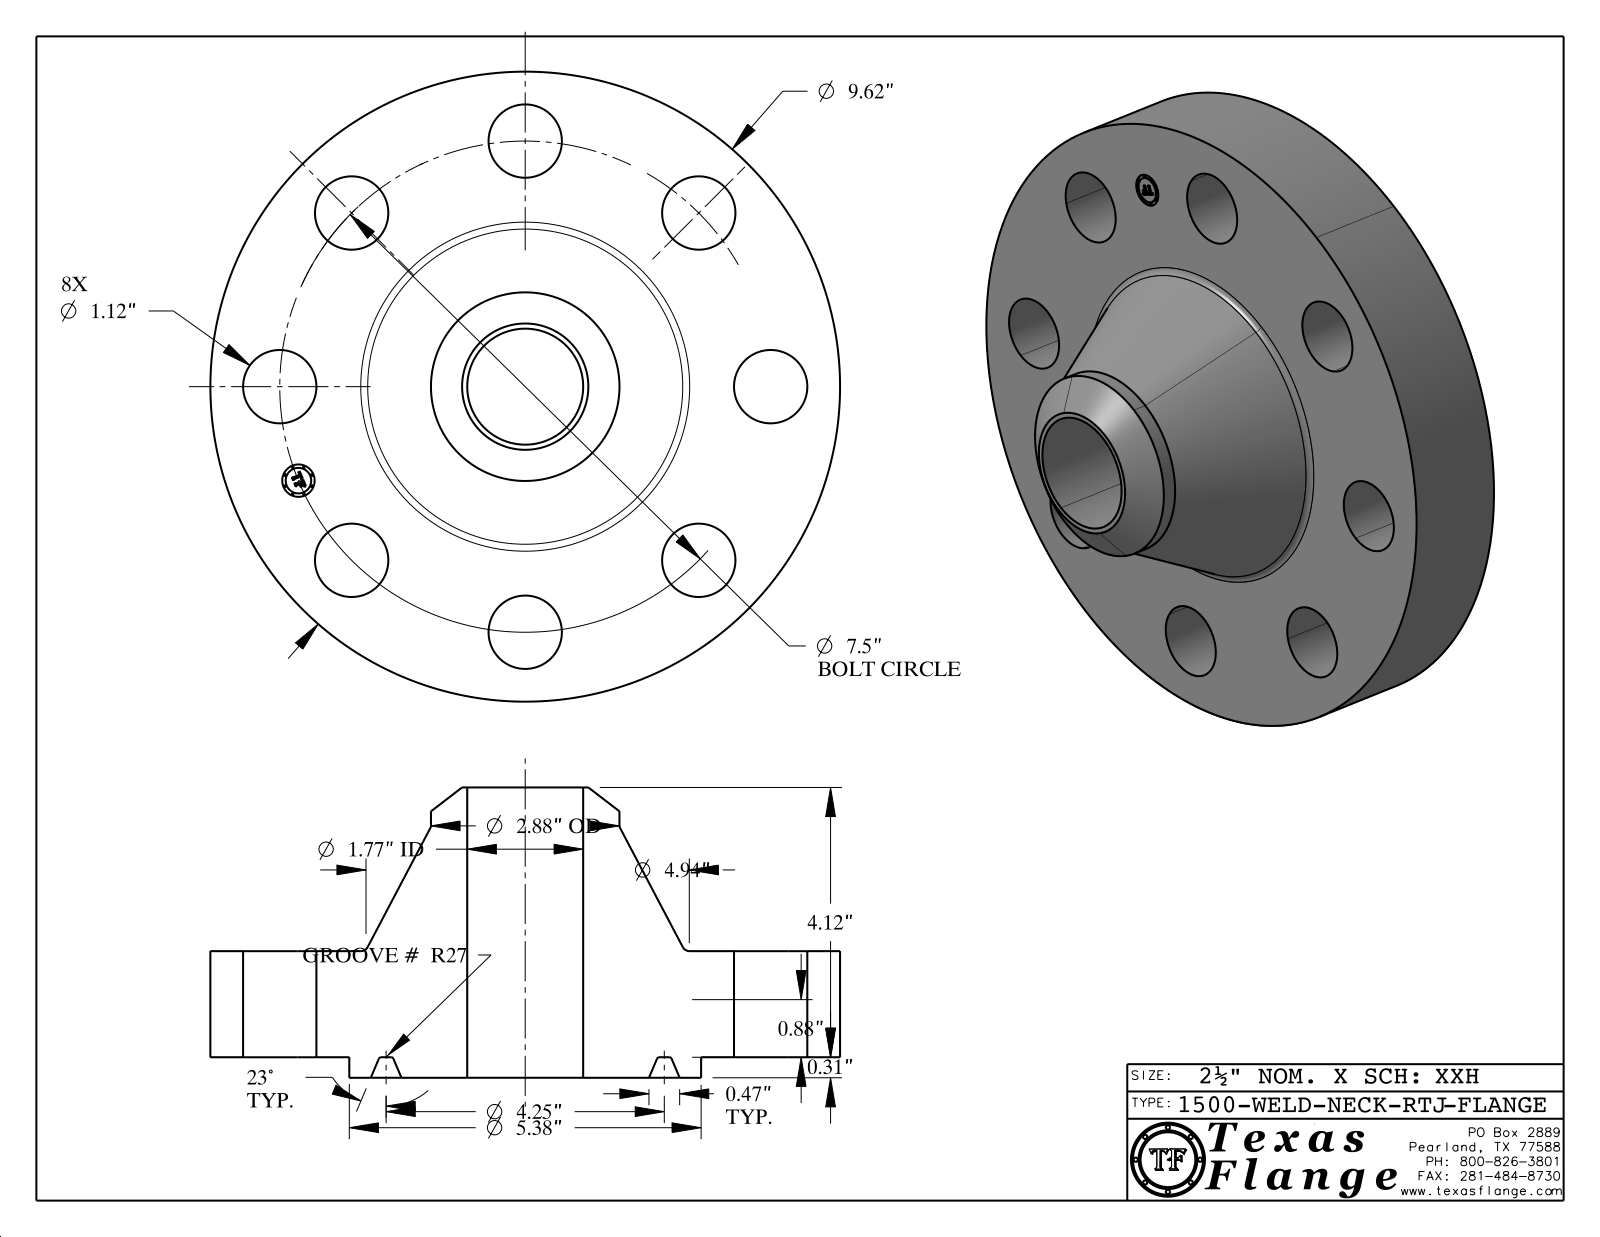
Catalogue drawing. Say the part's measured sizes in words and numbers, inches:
The part is named "1500-WELD-NECK-RTJ". Its 3-D file was written by "CATIA V5 STEP AP214 (AUTOMOTIVE_DESIGN)". It is 1 solid with 429 faces: 371 planar, 44 cylindrical and 14 other. Overall it measures 9.62 by 9.62 by 4.433 inches. Its volume is 125.9 cubic inches and its surface area 271.5 square inches. Round holes: 8 of diameter 1.12, 1 of diameter 0.495, 1 of diameter 1.771. Round bosses or shafts: 8 of diameter 0.03, 1 of diameter 9.62, 1 of diameter 5.375, 1 of diameter 2.88, 1 of diameter 0.39. The main face-to-face distances are 1.62, 0.313, 1.933, 4.433, 4.12, 2.5, 0.015, 1.918, 1.605, 2.515. The hole center spacings are 3.75, 2.87, 5.303, 6.929, 1.463, 6.236, 7.356, 7.5.
